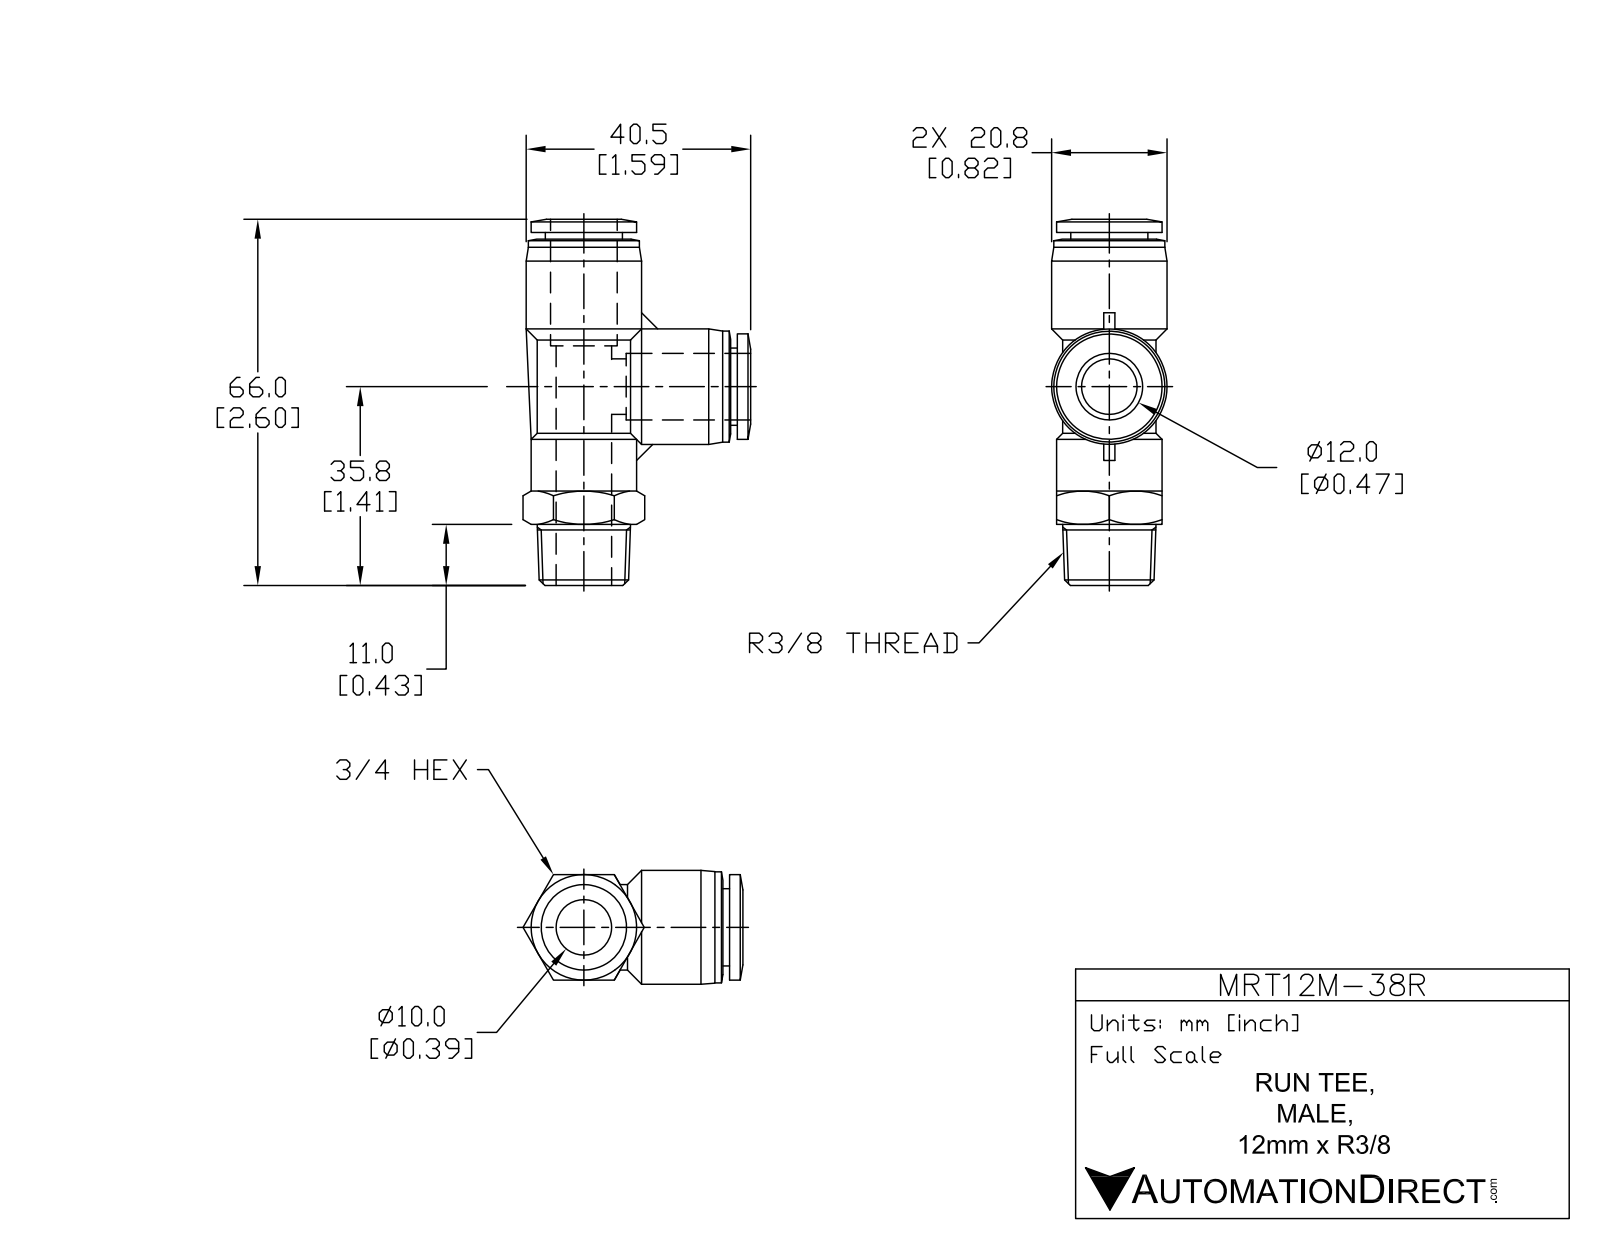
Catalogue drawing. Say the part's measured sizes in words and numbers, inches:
The part is named "MRT12M-38R". Its 3-D file was written by "SolidWorks 2015 (AUTOMOTIVE_DESIGN)". It is 1 solid with 99 faces: 24 planar, 32 cylindrical and 43 other. Overall it measures 2.6 by 1.619 by 0.819 inches. Its volume is 0.959 cubic inches and its surface area 14.72 square inches. Round holes: 2 of diameter 0.394, 2 of diameter 0.484. Round bosses or shafts: 2 of diameter 0.819, 2 of diameter 0.787, 2 of diameter 0.748, 2 of diameter 0.661, 2 of diameter 0.547. The main face-to-face distances are 0.748, 0.047, 0.76, 0.807, 2.506, 0.335, 0.413, 2.459, 0.433, 2.026.
